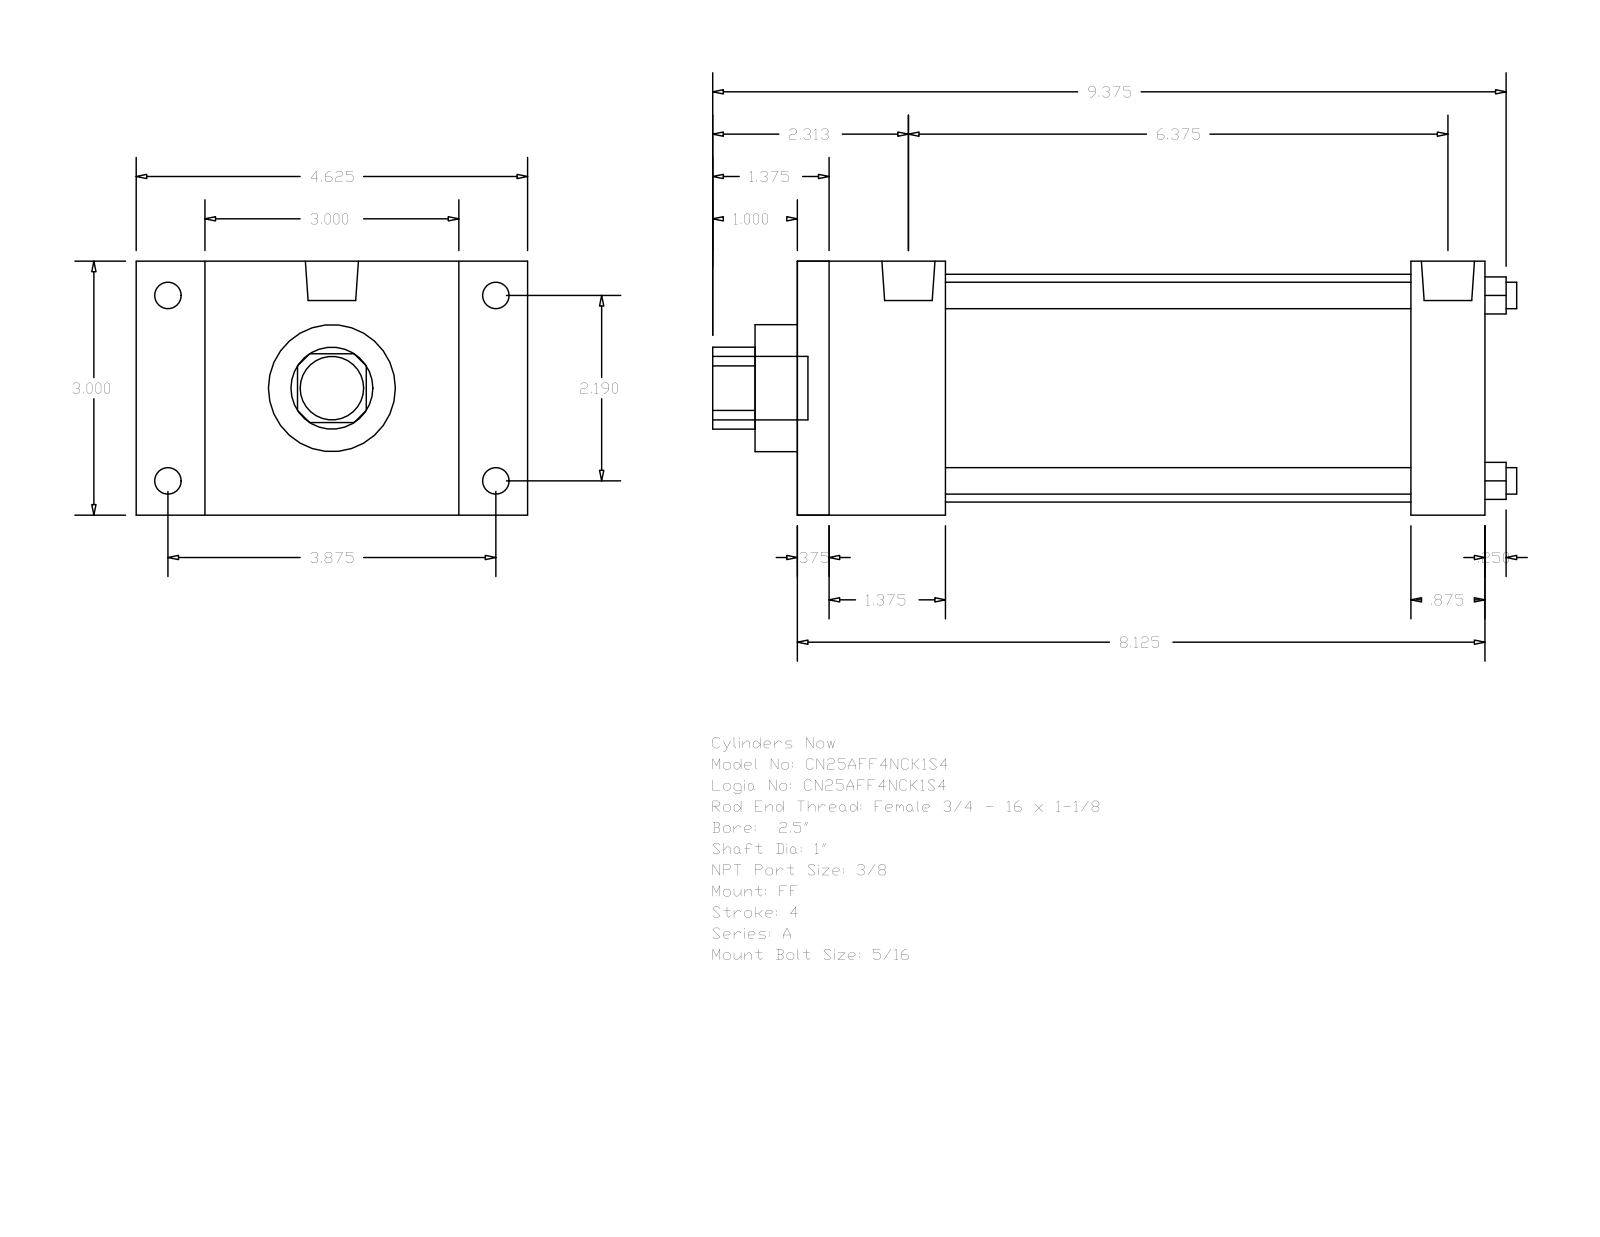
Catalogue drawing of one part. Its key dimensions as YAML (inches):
part_name: "A_FF__0250_1"
step_written_by: "GSSL Pune (CONFIG_CONTROL_DESIGN)"
units: inches
bodies: {solids: 0, faces: 92, planar: 64, cylindrical: 28, other: 0}
overall_size: [9.5, 4.625, 3]
round_holes:
  - {diameter: 0.313, count: 4}
  - {diameter: 1, count: 1}
  - {diameter: 1.5, count: 1}
  - {diameter: 2.69, count: 1}
round_bosses_or_shafts:
  - {diameter: 0.313, count: 4}
  - {diameter: 0.219, count: 4}
  - {diameter: 0.627, count: 2}
  - {diameter: 0.75, count: 1}
partial_cylinders:
  - {radius: 0.484, count: 1}
face_to_face_distances: [3, 8.125, 0.375, 7.75, 1.75, 7.25, 1.375, 6.875, 5.5, 6.375]
hole_center_spacings: [1.548, 2.19, 3.097]
